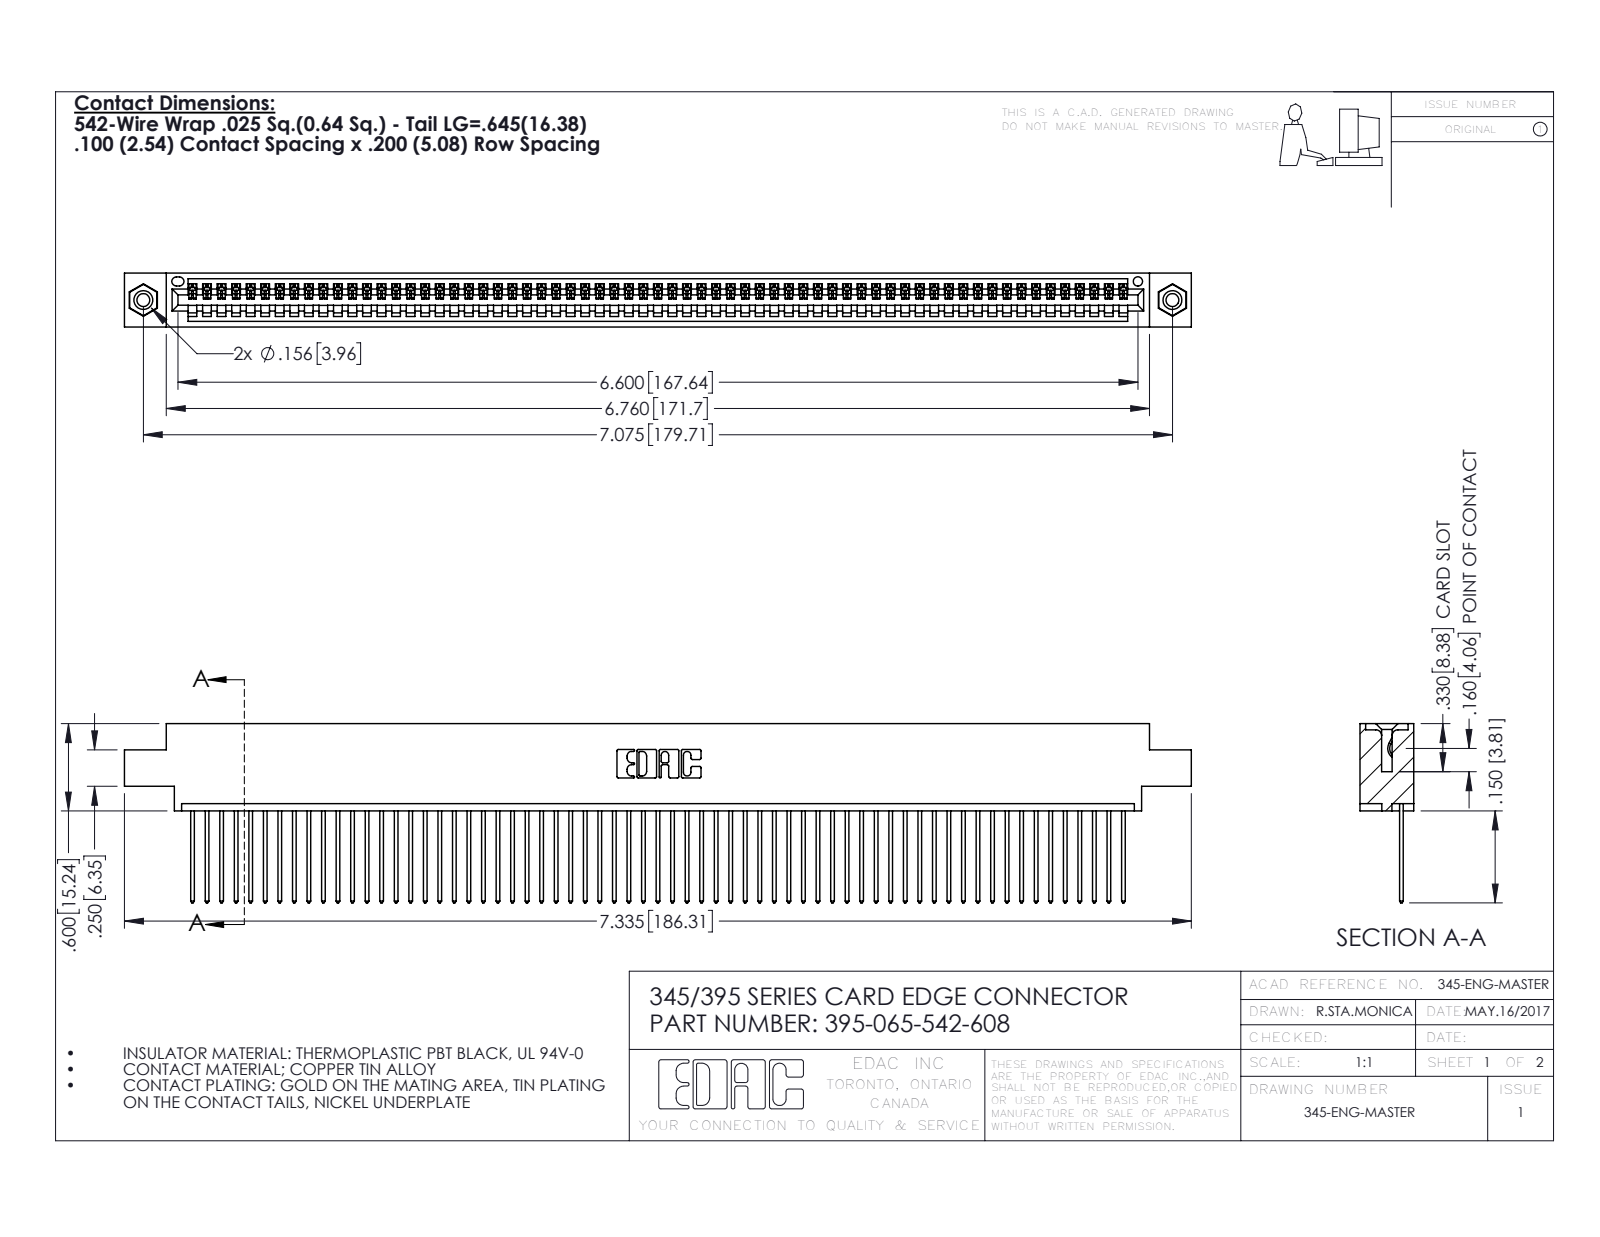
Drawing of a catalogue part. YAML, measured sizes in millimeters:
part_name: "395-065-542-608; 345-250-001_345-250-003-102; 345-292-001_345-293-142; 345 Part_0.170 Offset - 0.156 Dia-TI"
step_written_by: "SolidWorks 2016 (CONFIG_CONTROL_DESIGN)"
units: millimeters
bodies: {solids: 68, faces: 3960, planar: 2716, cylindrical: 1228, other: 16}
overall_size: [186.3, 31.3, 9.4]
volume: 17910
surface_area: 25170
round_holes:
  - {diameter: 2.3, count: 2}
  - {diameter: 3.2, count: 2}
  - {diameter: 4, count: 2}
  - {diameter: 1.6, count: 1}
round_bosses_or_shafts:
  - {diameter: 3.9, count: 2}
partial_cylinders:
  - {radius: 0.2, count: 130}
  - {radius: 0.3, count: 130}
  - {radius: 0.3, count: 22}
  - {radius: 0.2, count: 6}
  - {radius: 0.8, count: 6}
  - {radius: 0.7, count: 3}
  - {radius: 0.8, count: 2}
  - {radius: 1, count: 2}
face_to_face_distances: [1.8, 7.6, 9.4, 2.5, 6.9, 0.6, 5.1, 5.7, 4.4, 3.8]
hole_center_spacings: [6.9, 173.7, 179.7]
